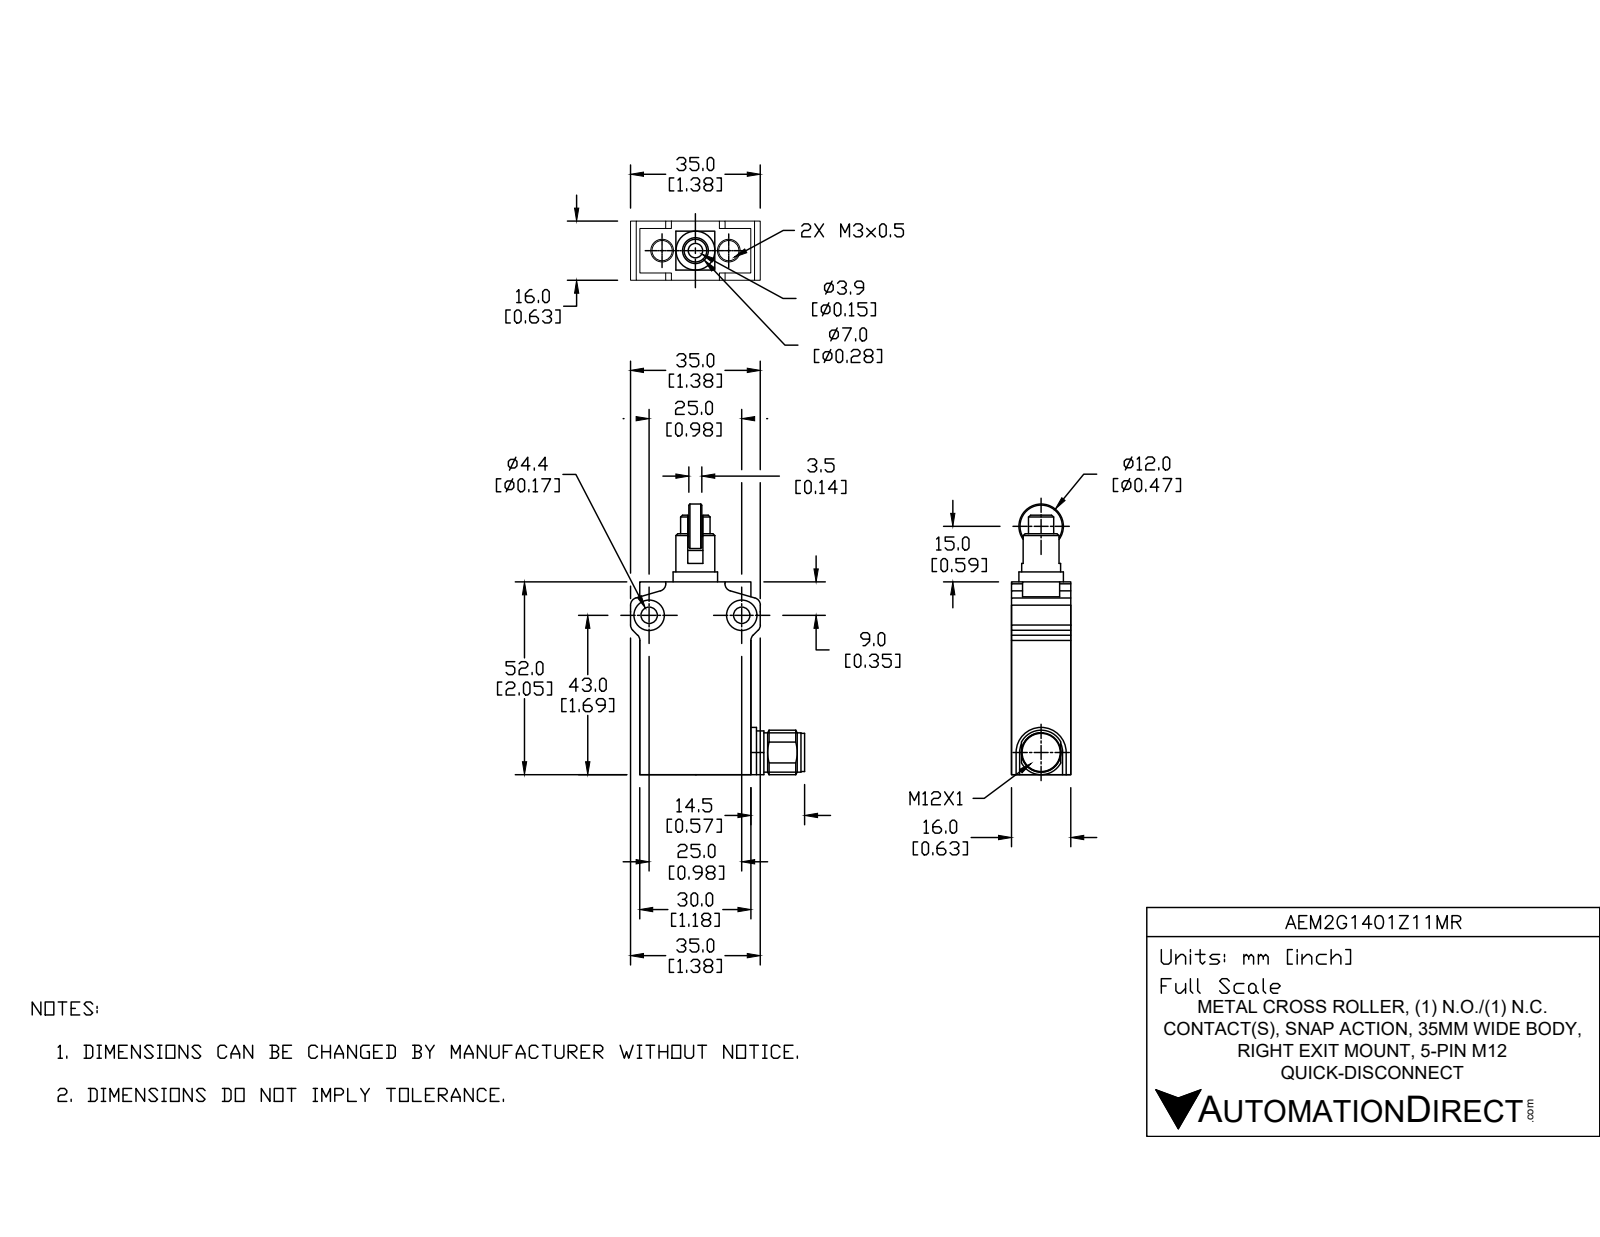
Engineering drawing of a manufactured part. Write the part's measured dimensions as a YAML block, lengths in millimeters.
part_name: "AEM2G1401Z11MR"
step_written_by: "SolidWorks 2019 (AUTOMOTIVE_DESIGN)"
units: millimeters
bodies: {solids: 5, faces: 157, planar: 68, cylindrical: 51, other: 38}
overall_size: [73.1, 46.5, 16]
volume: 26940
surface_area: 9619
round_holes:
  - {diameter: 3, count: 2}
  - {diameter: 4.4, count: 2}
  - {diameter: 8.2, count: 2}
  - {diameter: 8.1, count: 1}
round_bosses_or_shafts:
  - {diameter: 12, count: 3}
  - {diameter: 10.6, count: 1}
  - {diameter: 10.5, count: 1}
  - {diameter: 10.3, count: 1}
  - {diameter: 8, count: 1}
  - {diameter: 5.6, count: 1}
partial_cylinders:
  - {radius: 2, count: 8}
  - {radius: 6.5, count: 1}
face_to_face_distances: [16, 30, 52, 12, 4, 3.8, 13, 17, 2.5, 15.4]
hole_center_spacings: [9.5, 19, 25]
